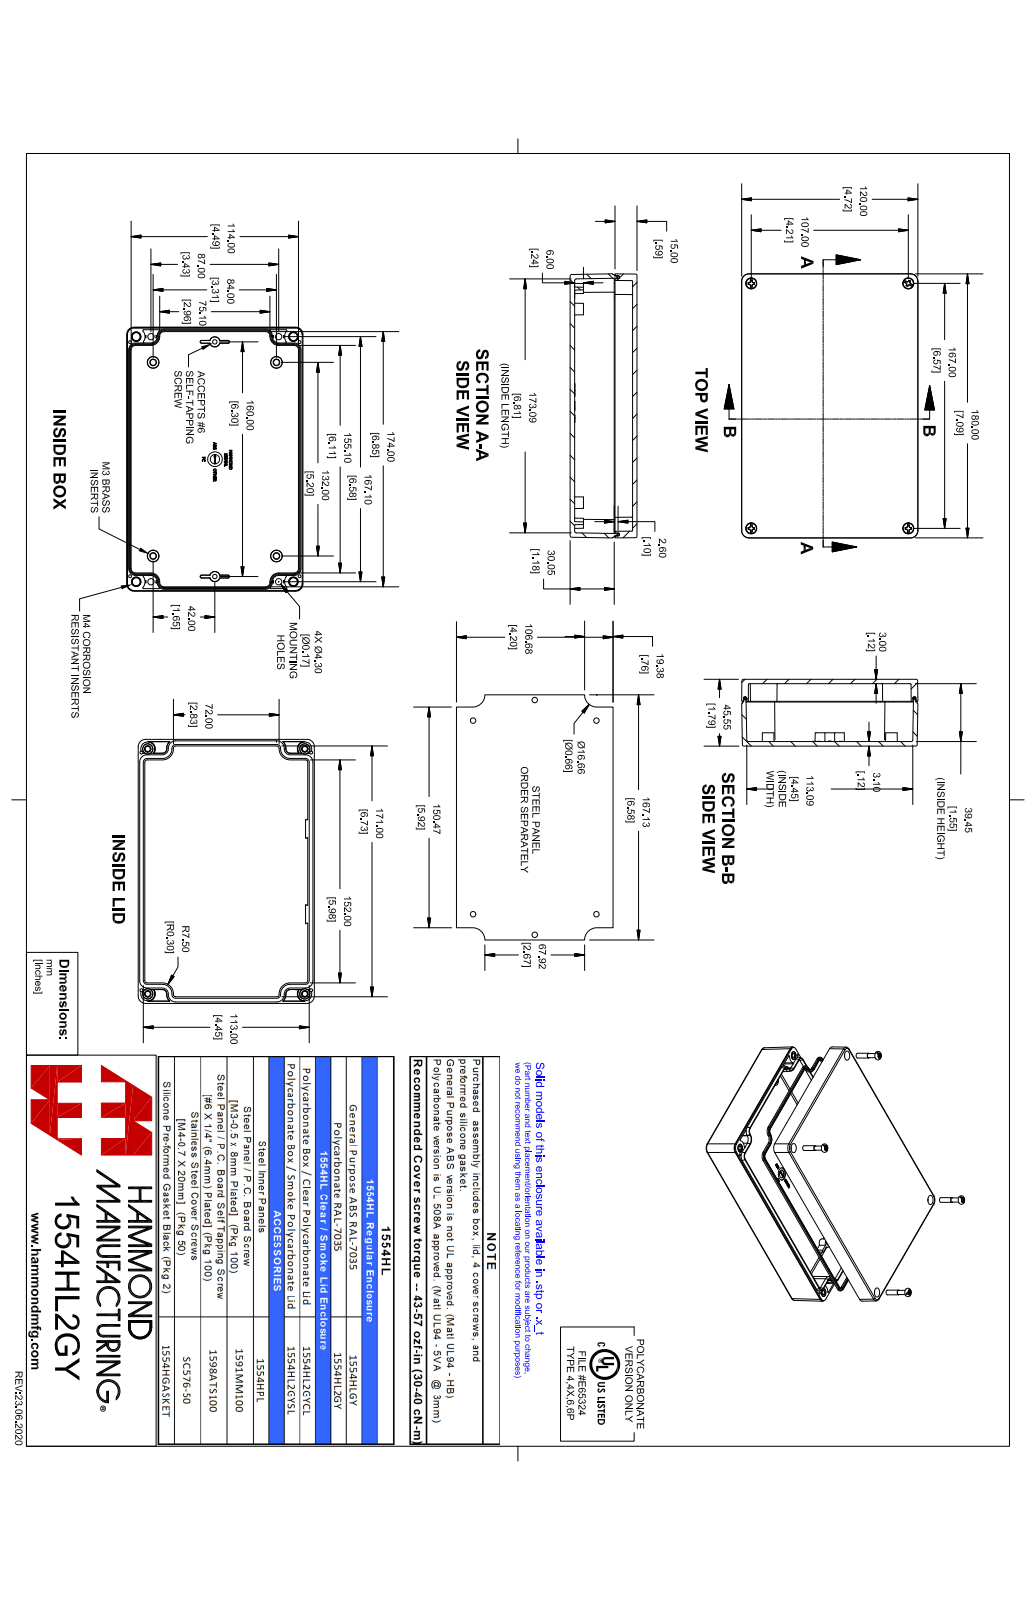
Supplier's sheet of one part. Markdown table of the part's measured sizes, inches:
| quantity | value |
| --- | --- |
| part name | 1554HL2GY |
| STEP written by | SolidWorks 2021 (AUTOMOTIVE_DESIGN) |
| units | inches |
| bodies | 15 solids, 1478 faces (374 planar, 340 cylindrical, 764 other) |
| overall size | 7.089 × 4.727 × 1.793 |
| volume | 13.46 in³ |
| surface area | 242.3 in² |
| round holes (diameter × count) | 0.079 × 4, 0.097 × 4, 0.128 × 4, 0.138 × 4, 0.181 × 4, 0.276 × 4 |
| round bosses / shafts (diameter × count) | 0.25 × 4, 0.218 × 4, 0.21 × 4, 0.19 × 4, 0.154 × 4, 0.153 × 4, 0.15 × 4, 0.135 × 4 |
| partial cylindrical surfaces (radius × count) | 0.02 × 36, 0.039 × 18, 0.197 × 8, 0.031 × 4, 0.118 × 4, 0.187 × 4 |
| main face-to-face distances | 1.793, 0.118, 0.122, 1.671, 1.675, 1.553, 0.12, 0.177, 0.059, 0.472 |
| hole center spacings | 0.197, 0.824, 0.859, 3.822, 3.974, 4.384, 5.821, 5.903 |
